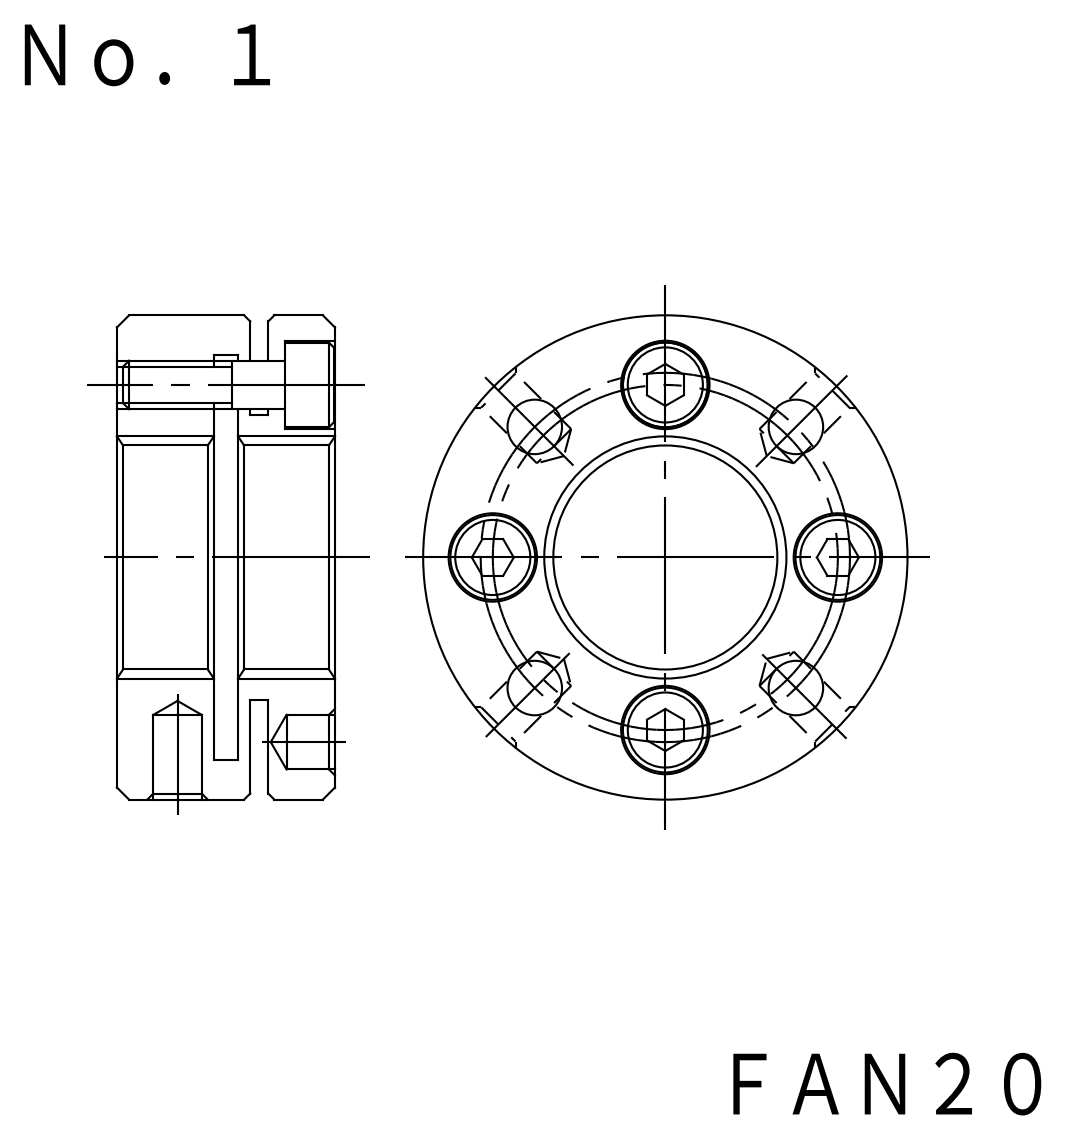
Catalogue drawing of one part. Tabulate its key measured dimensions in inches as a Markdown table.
| quantity | value |
| --- | --- |
| part name | FKD FAN20; M4X12_default |
| STEP written by | SolidWorks 2012 (CONFIG_CONTROL_DESIGN) |
| units | inches |
| bodies | 5 solids, 142 faces (50 planar, 76 cylindrical, 16 other) |
| overall size | 1.575 × 1.575 × 0.709 |
| volume | 0.849 in³ |
| surface area | 16.43 in² |
| round holes (diameter × count) | 0.128 × 4, 0.169 × 4, 0.177 × 4, 0.287 × 4, 0.157 × 2, 0.787 × 1, 1.398 × 1 |
| round bosses / shafts (diameter × count) | 0.276 × 4, 0.157 × 4, 1.575 × 1, 1.004 × 1 |
| main face-to-face distances | 0.315, 0.394, 0.709, 0.433, 0.276, 0.492, 0.059, 0.217, 0.079, 0.118 |
| hole center spacings | 0.459, 0.6, 1.109, 0.849, 0.849, 1.2, 1.201 |
